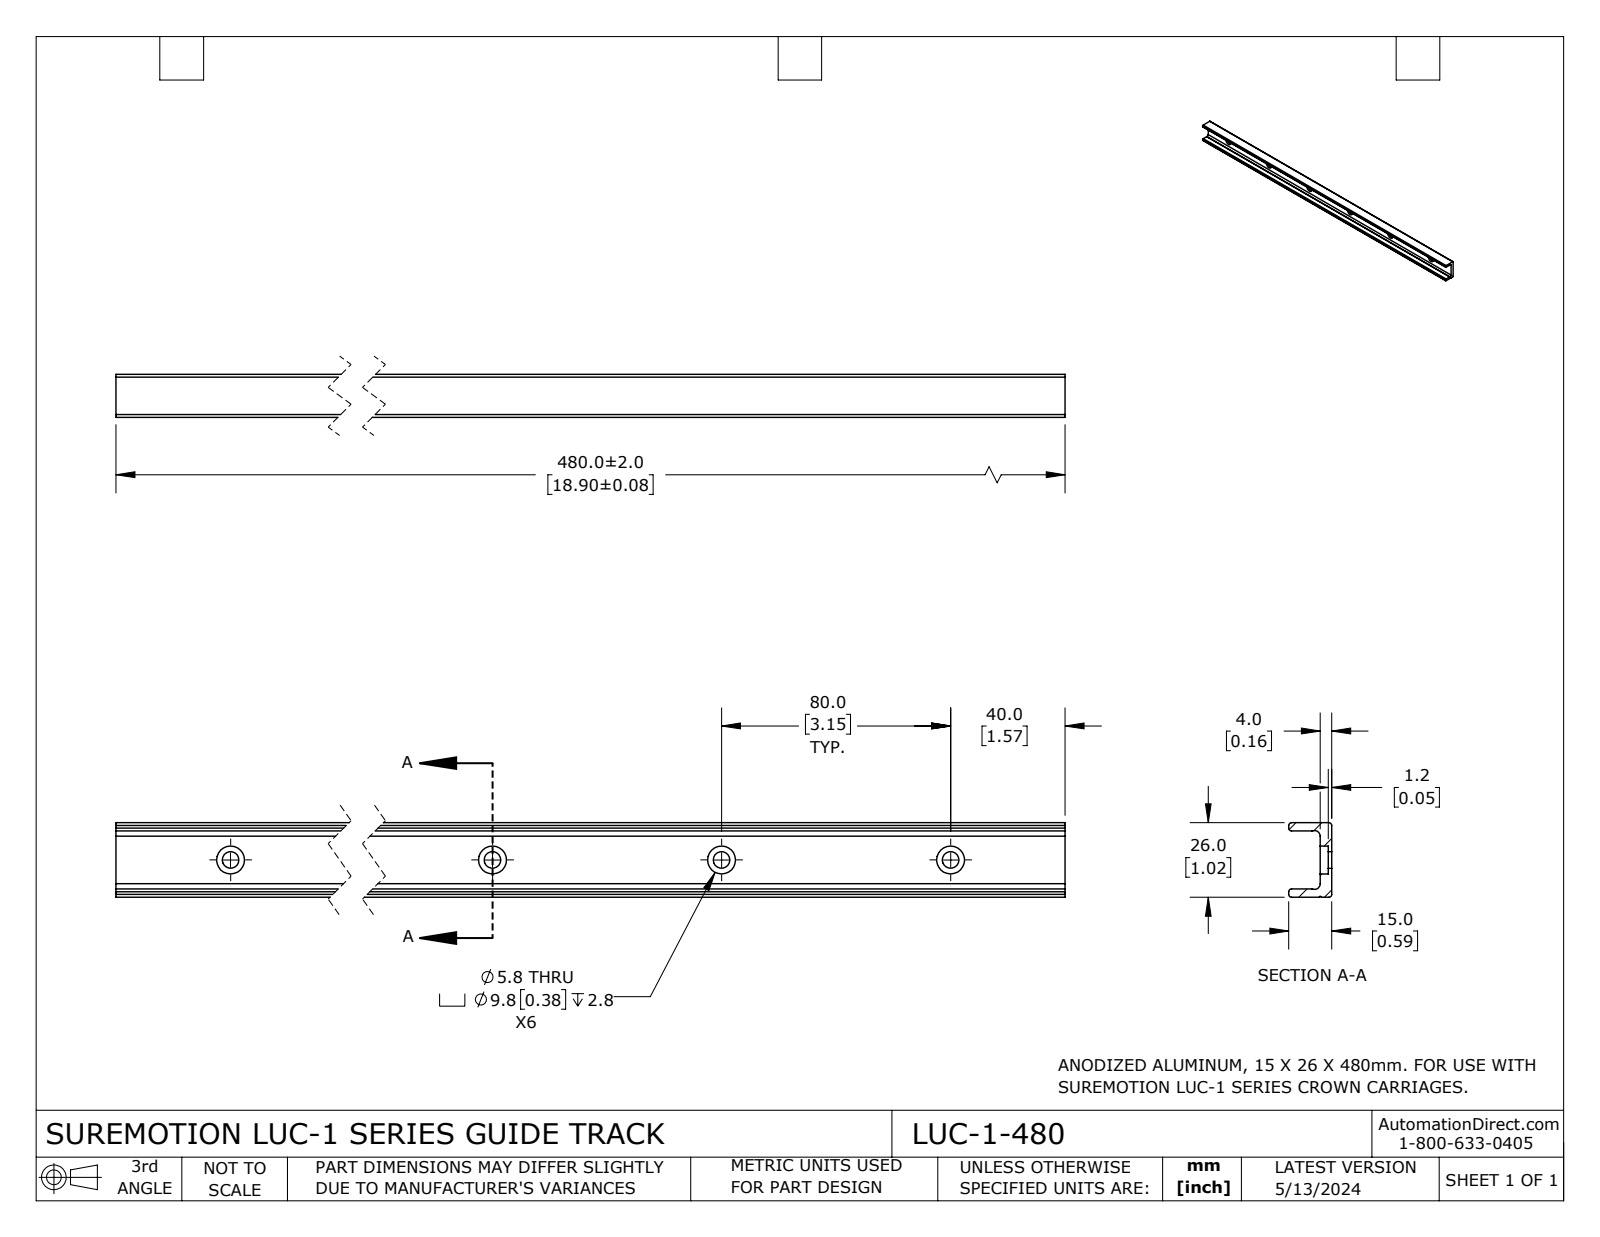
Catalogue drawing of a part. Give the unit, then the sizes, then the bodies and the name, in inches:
Units: inches
Overall size (bounding box): 18.898 × 1.024 × 0.591
Round holes (diameter × count): ⌀0.228 ×6, ⌀0.384 ×6
Partial cylindrical surfaces — rounded edges, fillets, slot ends (radius × count): R0.039 ×8, R0.078 ×2, R0.013 ×1
Main face-to-face distances: 0.158, 0.114, 0.91, 1.024, 0.796, 0.591, 0.433, 0.048, 0.11, 0.544
Hole centre spacings: 3.15, 6.299, 9.449, 12.598, 15.748
Volume: 4.818 in³ · Surface area: 75.8 in²
Bodies: 1 solid, 52 faces (17 planar, 35 cylindrical, 0 other)
Part name (STEP PRODUCT): LUC-1-480
STEP written by: SolidWorks 2023 (CONFIG_CONTROL_DESIGN)
